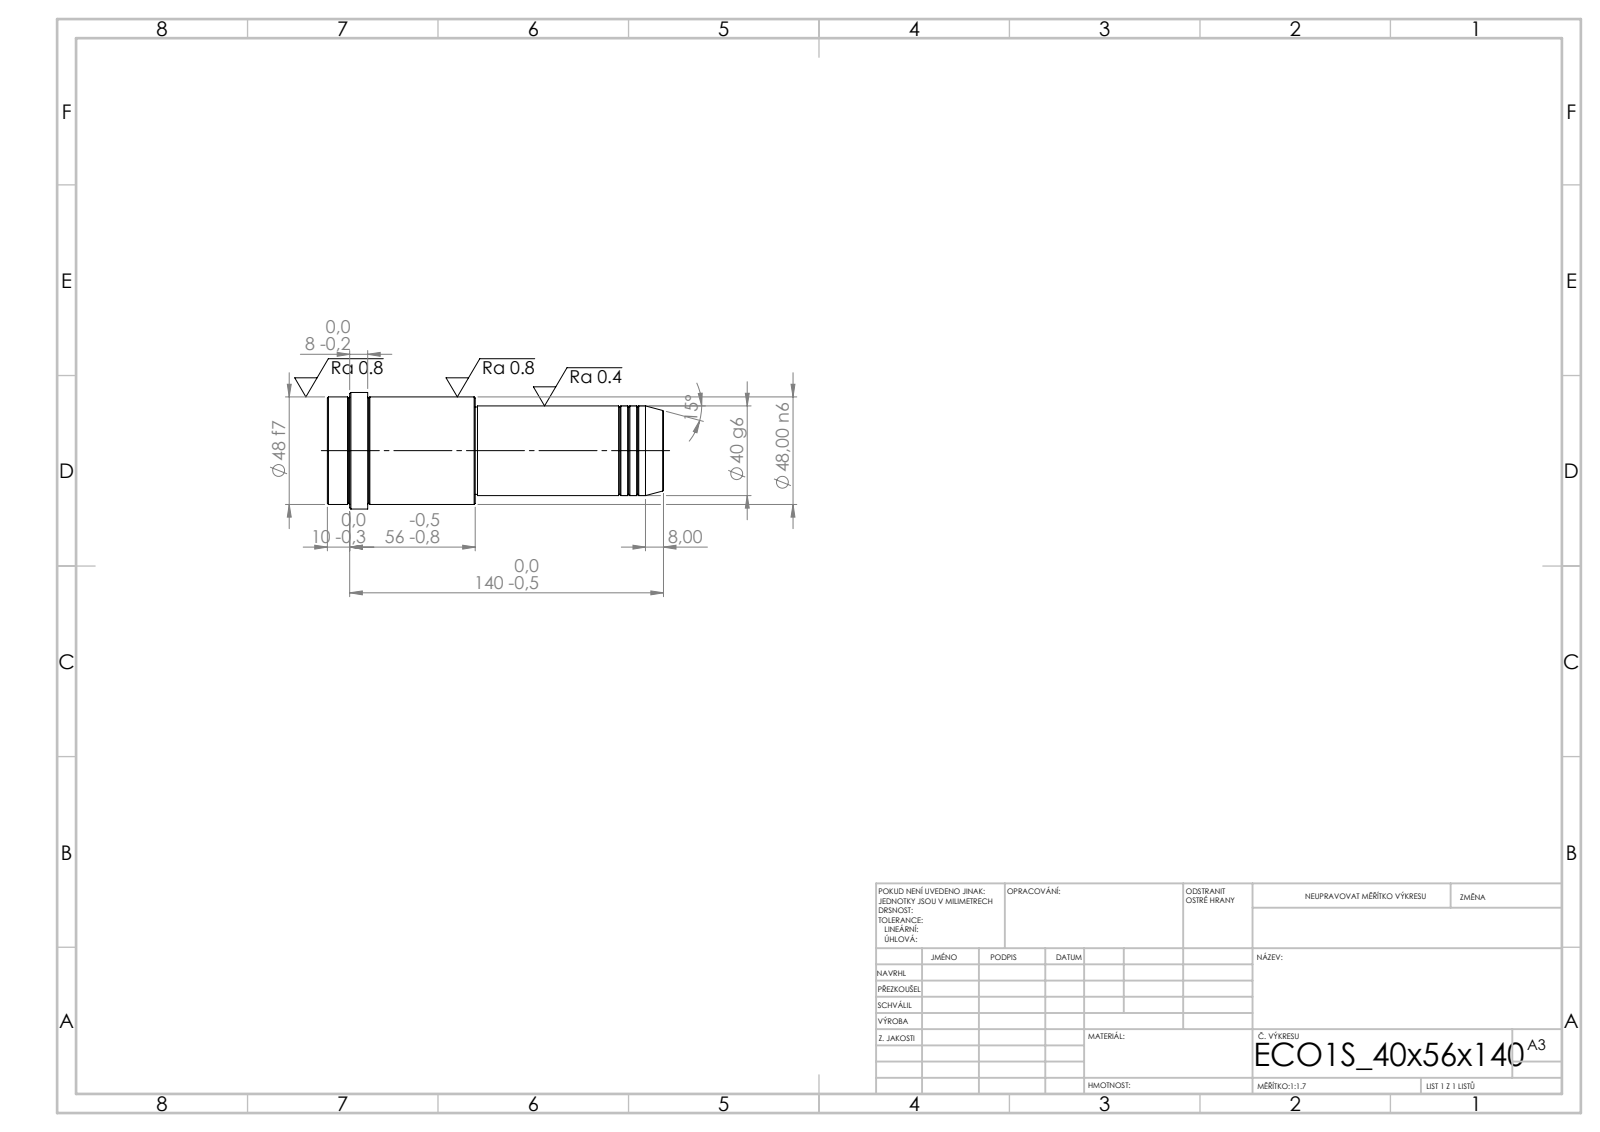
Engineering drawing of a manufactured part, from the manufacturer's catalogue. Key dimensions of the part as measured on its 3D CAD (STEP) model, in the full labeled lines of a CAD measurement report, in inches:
STEP written by: SolidWorks 2019 (CONFIG_CONTROL_DESIGN)
Units: inches
Bodies: 1 solid, 52 faces (6 planar, 16 cylindrical, 30 other)
Overall size (bounding box): 5.906 × 2.047 × 2.047
Volume: 13.8 in³ · Surface area: 38.63 in²
Round bosses / shafts (diameter × count): ⌀2.047 ×1, ⌀1.89 ×1, ⌀1.575 ×1, ⌀1.535 ×1
Main face-to-face distances: 5.906, 3.307, 2.598, 5.197, 1.89, 0.709, 5.512, 2.205, 0.315, 0.394
